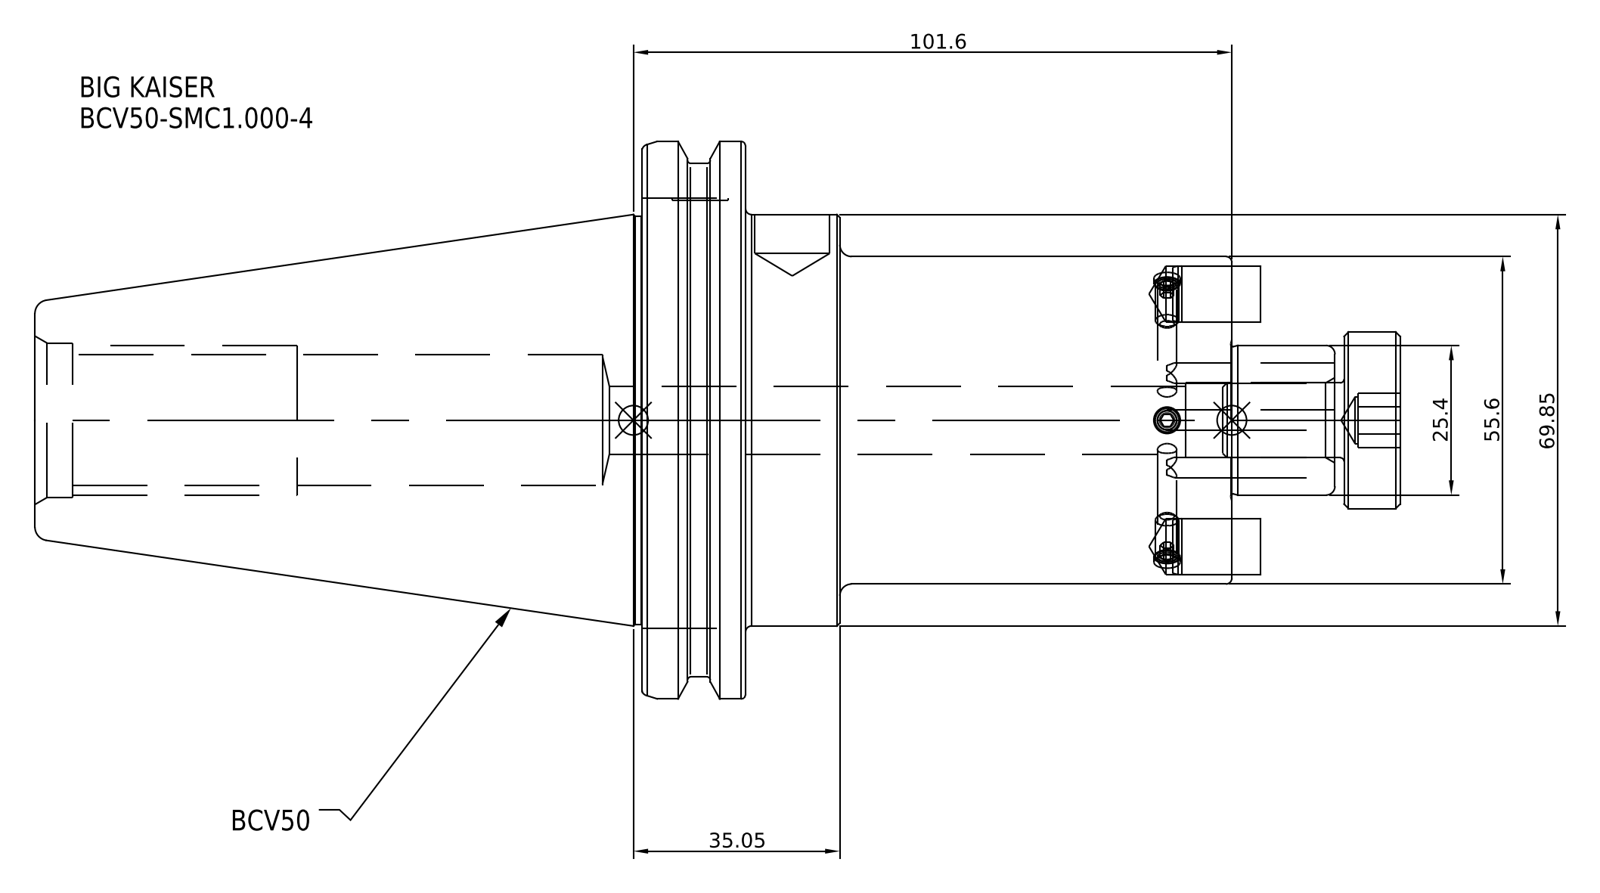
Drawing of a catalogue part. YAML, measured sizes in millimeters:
part_name: "BCV50-SMC1_000-4"
step_written_by: "SolidWorks 2021 (CONFIG_CONTROL_DESIGN)"
units: millimeters
bodies: {solids: 1, faces: 38, planar: 18, cylindrical: 14, other: 6}
overall_size: [208.1, 98.43, 98.43]
volume: 598220
surface_area: 55388
round_holes:
  - {diameter: 11.51, count: 1}
round_bosses_or_shafts:
  - {diameter: 98.43, count: 1}
  - {diameter: 91.29, count: 1}
  - {diameter: 69.85, count: 1}
  - {diameter: 55.6, count: 1}
face_to_face_distances: [17.55, 82.55, 100.1, 66.55, 16, 33.55, 203.2, 136.65, 120.65, 103.1]
